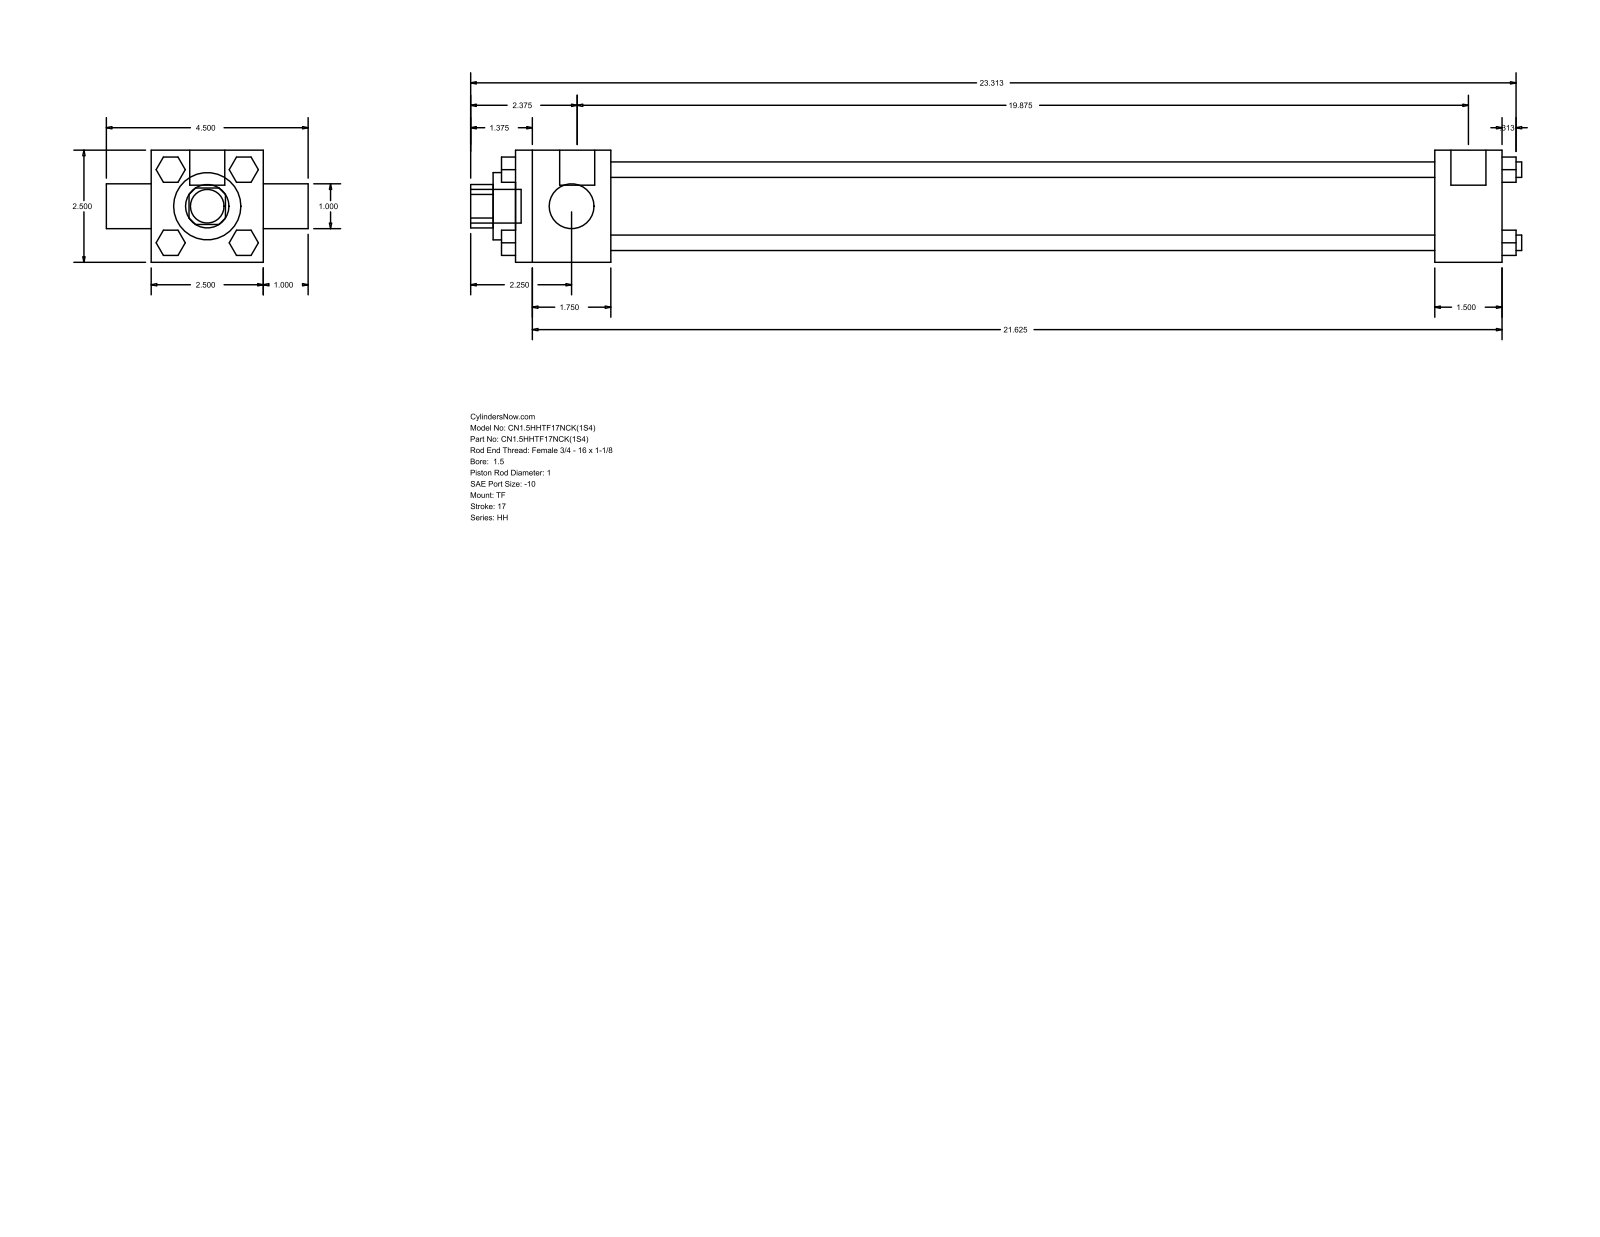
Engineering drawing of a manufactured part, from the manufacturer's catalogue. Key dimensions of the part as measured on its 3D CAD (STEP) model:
Part name (STEP PRODUCT): HH_TF__0150_1
STEP written by: GSSL Pune (CONFIG_CONTROL_DESIGN)
Units: millimetres
Bodies: 0 solids, 120 faces (92 planar, 28 cylindrical, 0 other)
Overall size (bounding box): 595.31 × 114.3 × 63.5
Round holes (diameter × count): ⌀25.4 ×2, ⌀38.1 ×1, ⌀44.45 ×1
Round bosses / shafts (diameter × count): ⌀8.76 ×4, ⌀5.56 ×3, ⌀19.84 ×2, ⌀19.05 ×1
Partial cylindrical surfaces — rounded edges, fillets, slot ends (radius × count): R12.29 ×1
Main face-to-face distances: 63.5, 504.82, 466.72, 38.1, 53.98, 520.7, 558.8, 566.74, 25.4, 20.7
